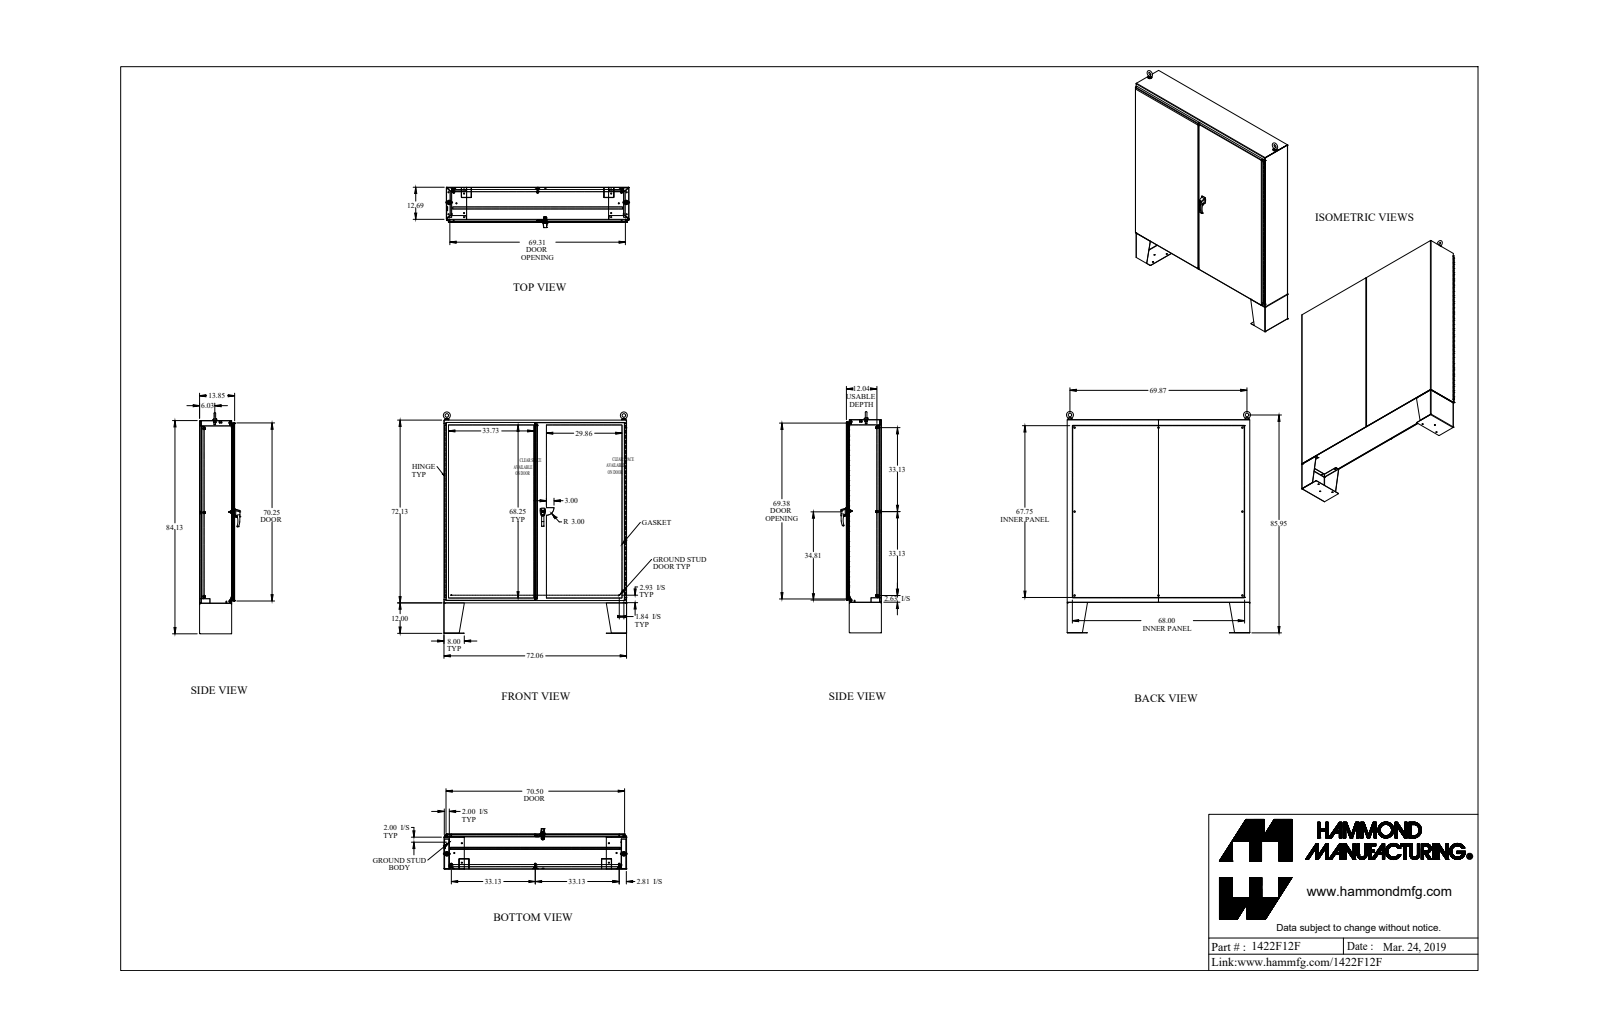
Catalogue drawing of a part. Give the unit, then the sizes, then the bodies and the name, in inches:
Units: inches
Overall size (bounding box): 87.778 × 73.121 × 15.963
Round holes (diameter × count): ⌀0.304 ×24, ⌀0.437 ×14, ⌀0.307 ×9, ⌀0.563 ×8, ⌀0.445 ×6, ⌀0.11 ×2, ⌀0.25 ×2, ⌀0.257 ×2, ⌀0.28 ×2, ⌀0.281 ×2, ⌀0.313 ×2, ⌀0.39 ×2
Round bosses / shafts (diameter × count): ⌀1 ×10, ⌀0.65 ×8, ⌀0.375 ×8, ⌀0.33 ×8, ⌀0.281 ×6, ⌀0.25 ×4, ⌀1.75 ×2, ⌀1.5 ×2
Partial cylindrical surfaces — rounded edges, fillets, slot ends (radius × count): R0.048 ×32, R0.143 ×32, R0.125 ×22, R0.018 ×16, R0.06 ×14, R0.116 ×12, R0.05 ×8, R0.185 ×8
Main face-to-face distances: 0.095, 0.125, 13.753, 13.628, 13.723, 13.848, 0.125, 1.687, 12.036, 11.941
Hole centre spacings: 6, 12, 18, 70.647, 24, 71.407, 66.25, 72.657
Volume: 2 431 in³ · Surface area: 44 983 in²
Bodies: 92 solids, 2997 faces (1372 planar, 1378 cylindrical, 247 other)
Part name (STEP PRODUCT): 1422F12F_Default
STEP written by: SolidWorks 2019 (CONFIG_CONTROL_DESIGN)
